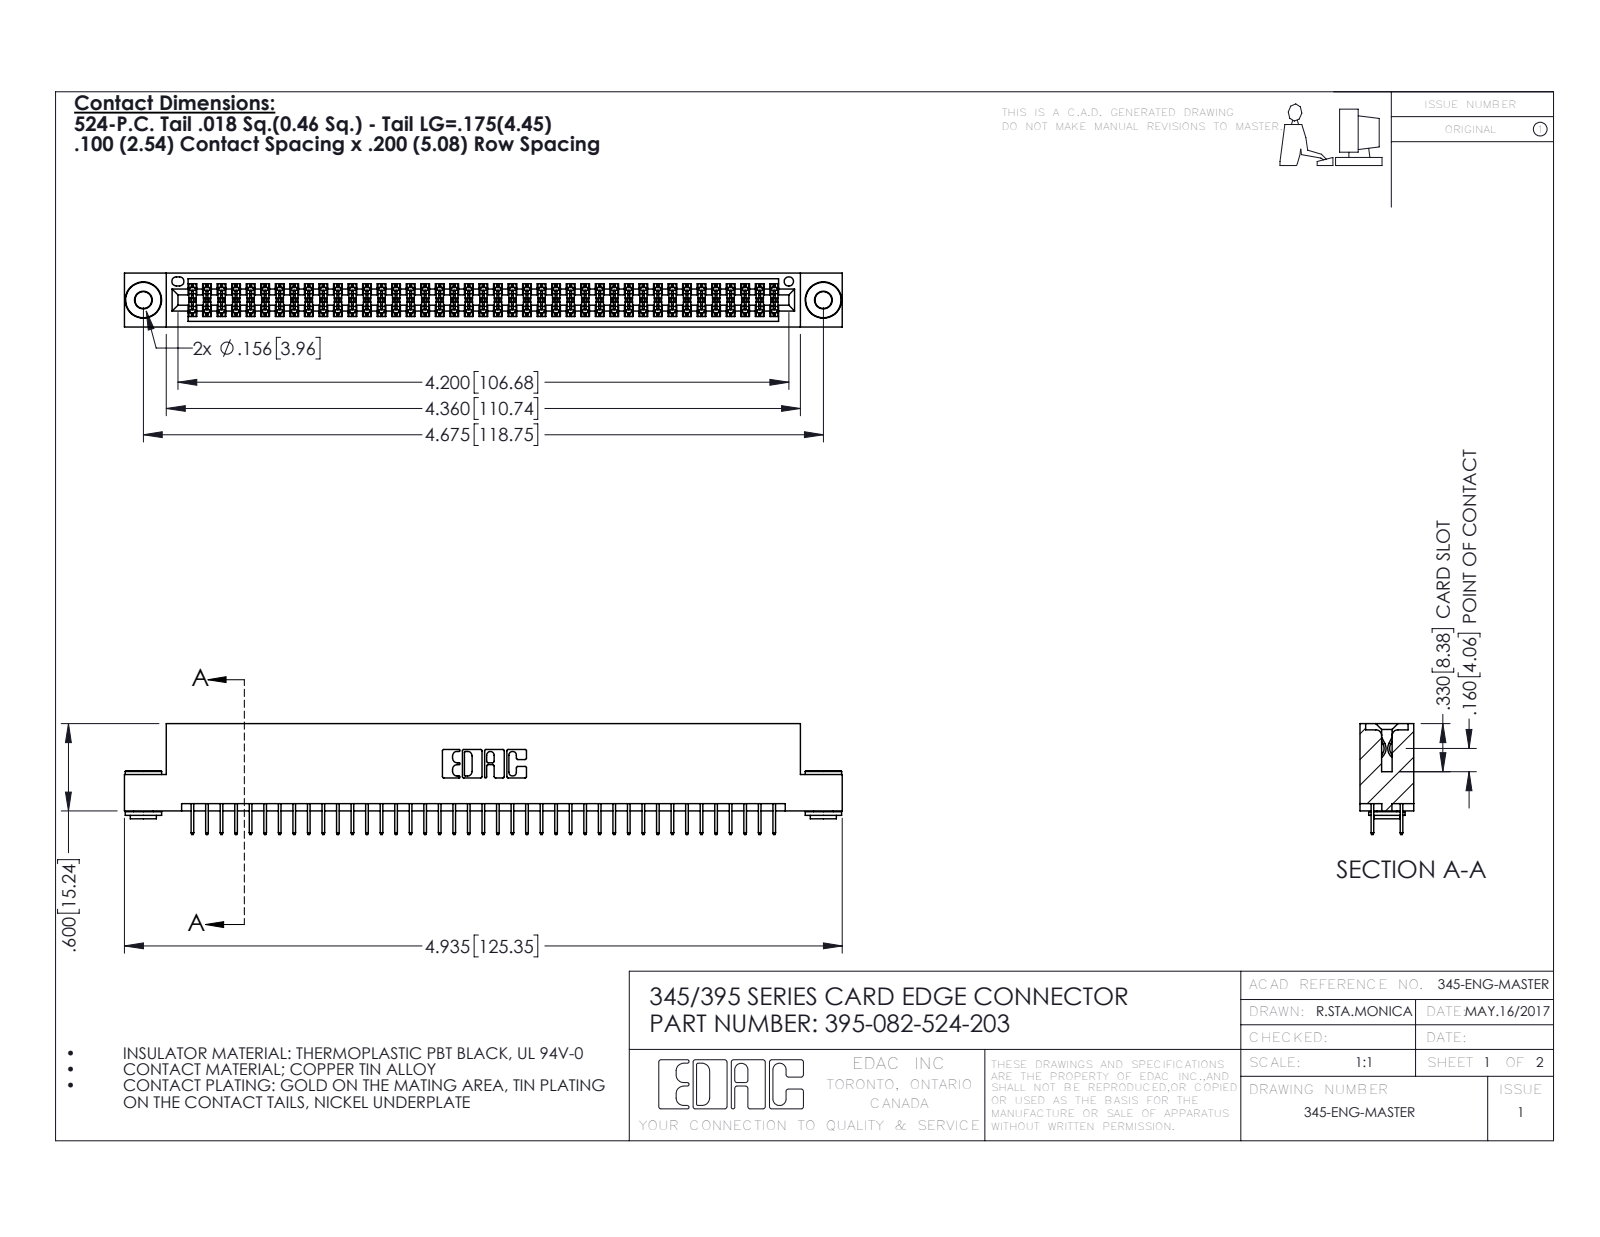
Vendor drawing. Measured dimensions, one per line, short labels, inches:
name: 345-292-001_345-293-124; 395-082-524-203; 345-250-002_345-250-002-102; 345 Part_Flush Mounting Lugs - 0.156 Dia-TH
written by: SolidWorks 2016 (CONFIG_CONTROL_DESIGN)
unit: in
bodies: 85 solids, 4592 faces (3288 planar, 1296 cylindrical, 8 other)
size: 4.935 × 0.762 × 0.37
volume: 0.736 in³; area: 27.42 in²
holes: 2× ⌀0.116, 2× ⌀0.156, 1× ⌀0.064
bosses: 2× ⌀0.25, 2× ⌀0.18, 2× ⌀0.136
rounds: 123× R0.006, 22× R0.01, 6× R0.007, 6× R0.031, 3× R0.026, 2× R0.014, 2× R0.019, 2× R0.022
face distances: 0.072, 0.298, 0.2, 0.37, 0.025, 0.098, 0.272, 0.225, 0.072, 0.175
hole spacings: 0.27, 4.439, 4.675
